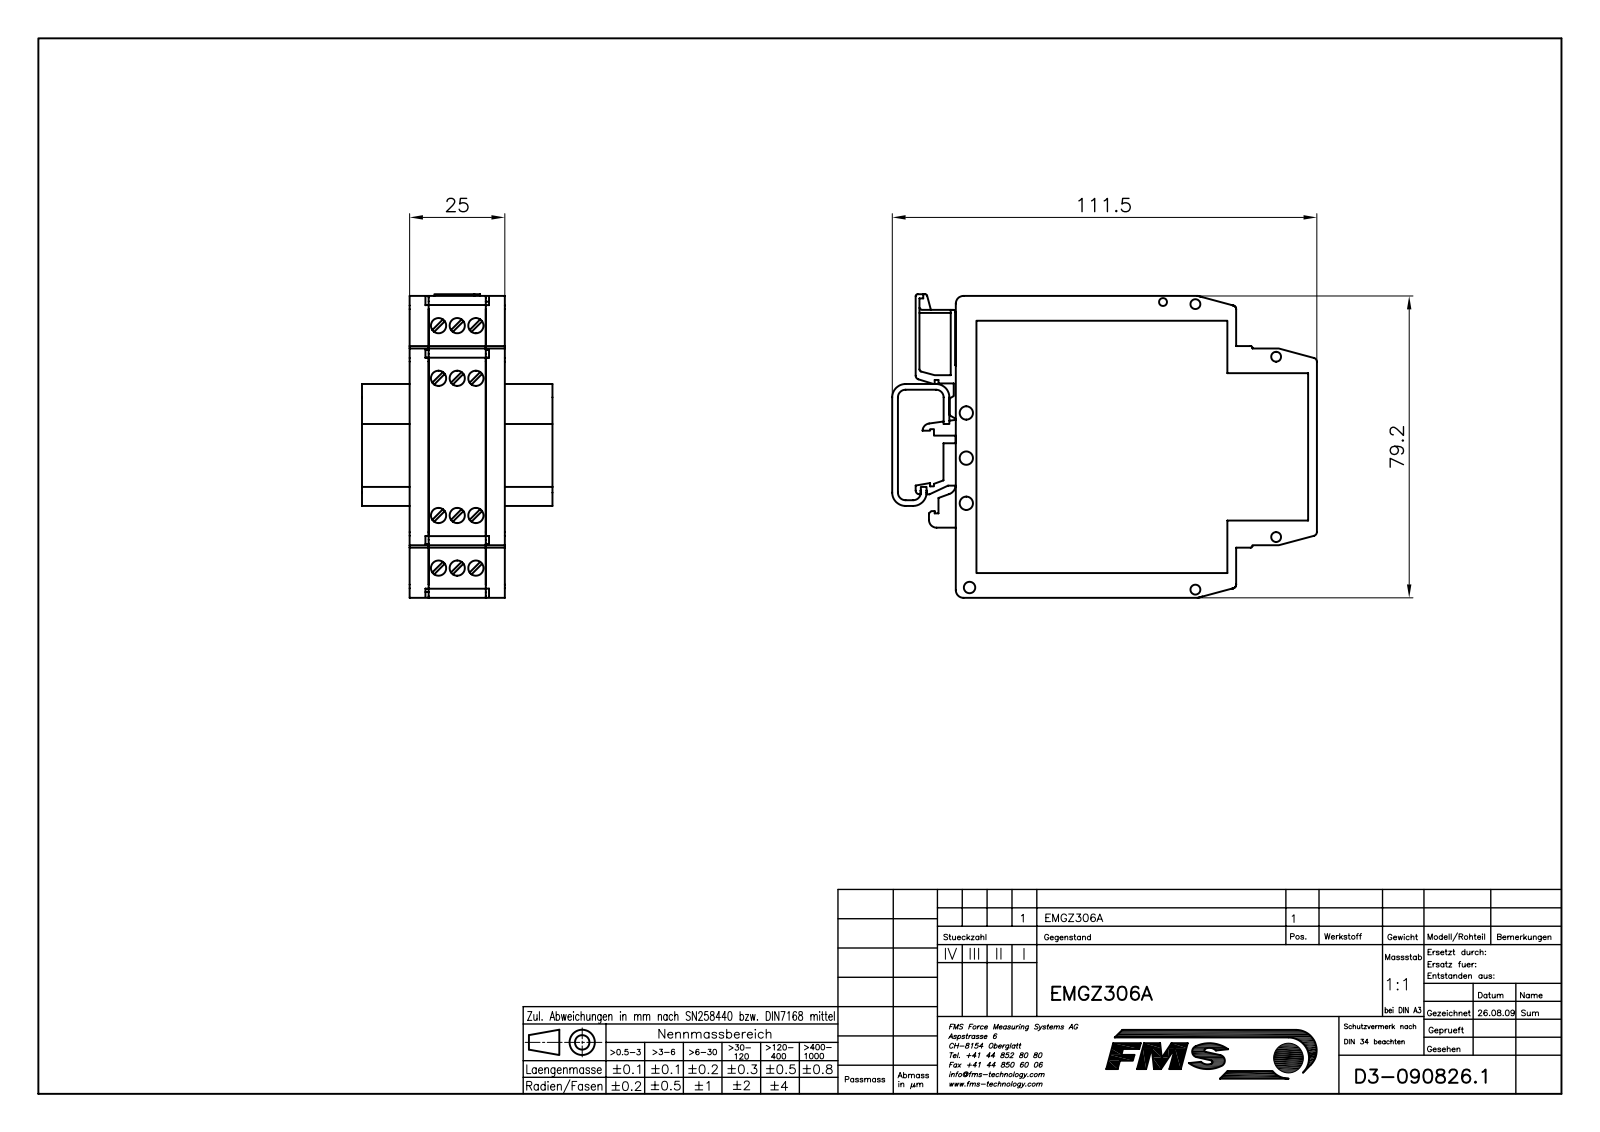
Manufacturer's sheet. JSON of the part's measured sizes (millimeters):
{"part_name": "E0908261; UEGH_25; UEGH_BE-MT_KPL_H.SELECT__00457947; UEGH-SE_5_H.SELECT__00457814.1 (+3 more)", "step_written_by": "Mechanical Desktop 2009 (CONFIG_CONTROL_DESIGN)", "units": "millimeters", "bodies": {"solids": 5, "faces": 1025, "planar": 763, "cylindrical": 262, "other": 0}, "overall_size": [111.5, 79.65, 50], "volume_mm3": 61042, "surface_area_mm2": 63142, "round_holes": [[4, 12], [3.5, 6], [2.6, 4], [3.1, 4], [2.08, 2], [3, 2]], "partial_cylinders_radius": [[1, 28], [0.5, 11], [0.17, 8], [0.3, 8], [2, 8], [1.25, 4], [3.5, 4], [1.5, 2]], "face_to_face_distances": [1.33, 23.27, 21.94, 24.6, 4.8, 18.47, 1.5, 19.8, 5, 20], "hole_center_spacings": [4.9, 14.64, 50.04, 13.8, 49.8, 9.8, 11.85, 16.93]}
